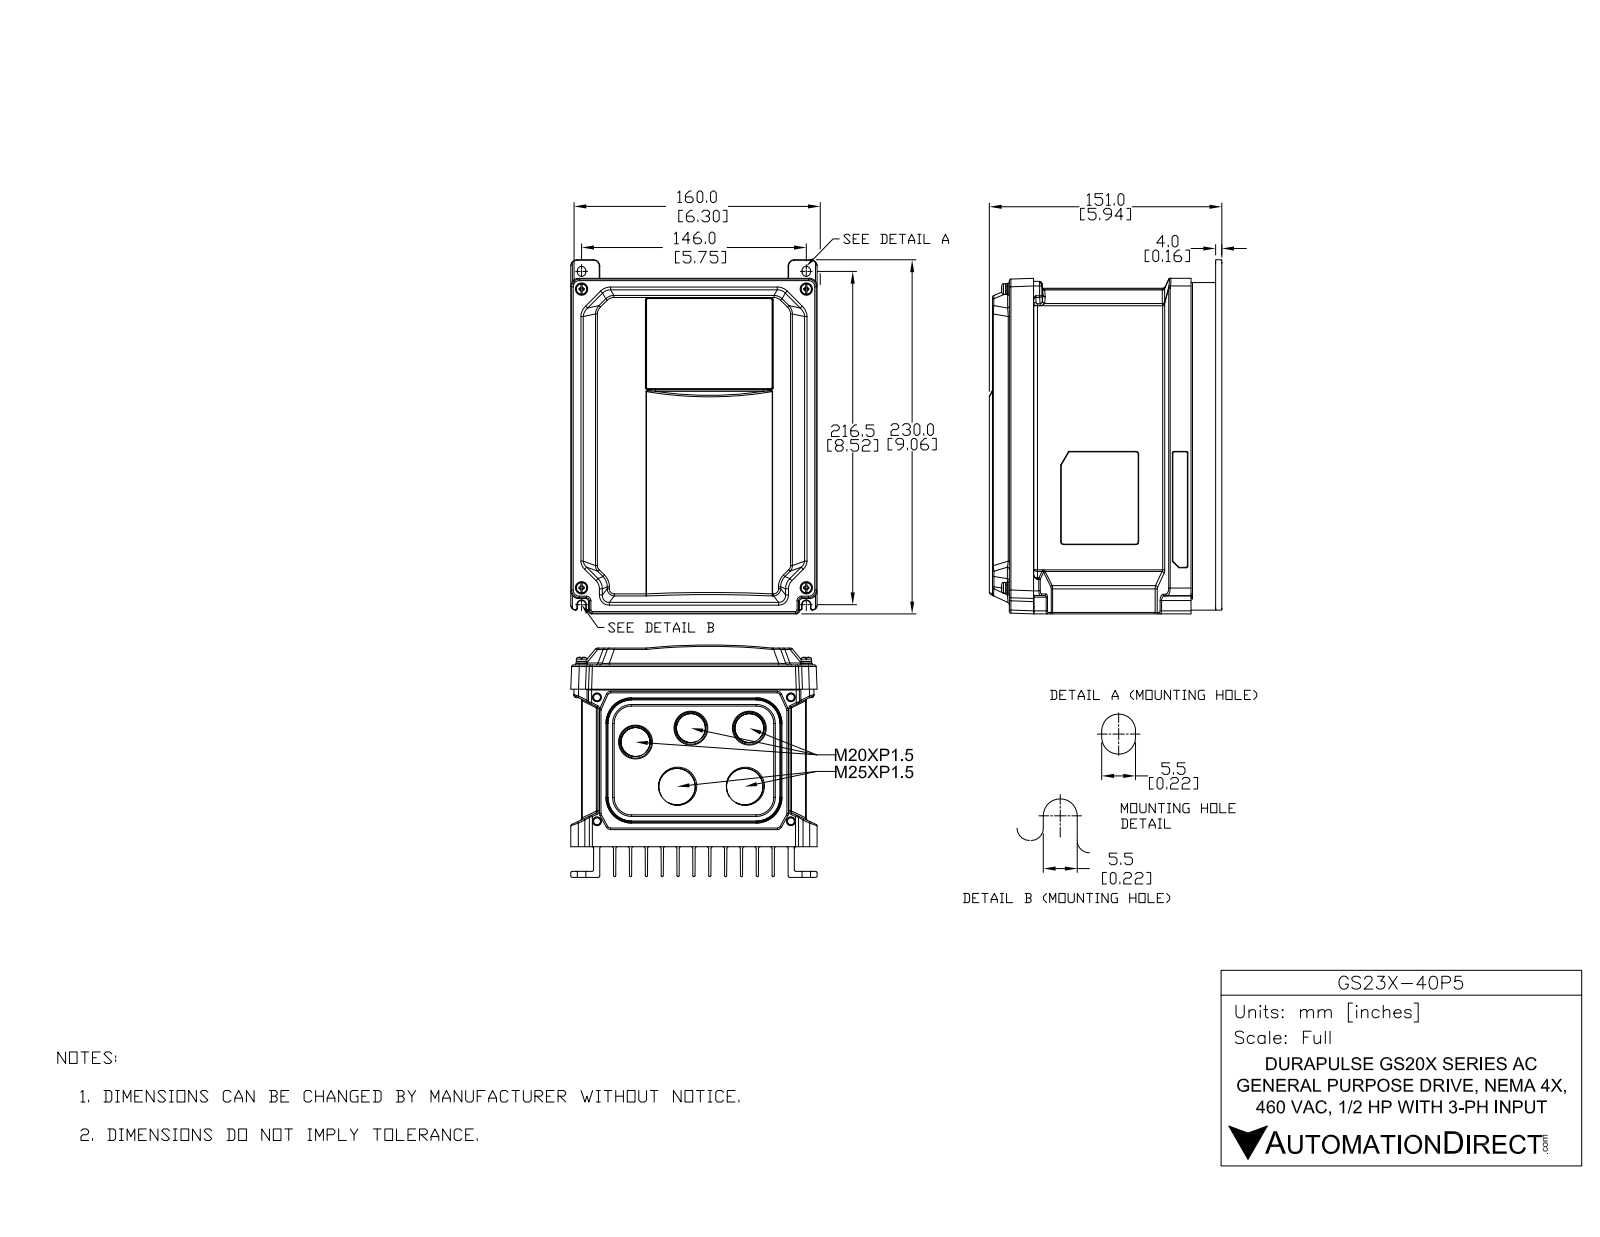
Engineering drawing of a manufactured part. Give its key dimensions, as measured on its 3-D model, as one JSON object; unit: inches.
{"part_name": "GS21X-20P5", "step_written_by": "SolidWorks 2017 (AUTOMOTIVE_DESIGN)", "units": "inches", "bodies": {"solids": 26, "faces": 4979, "planar": 3223, "cylindrical": 1019, "other": 737}, "overall_size": [9.26, 6.299, 5.945], "volume_in3": 53.16, "surface_area_in2": 832.5, "round_holes": [[0.098, 7], [0.165, 4], [0.591, 3], [0.822, 3], [0.827, 3], [0.13, 2], [0.15, 2], [1.015, 2]], "round_bosses_or_shafts": [[0.035, 8], [0.157, 5], [0.268, 4], [0.988, 3], [0.929, 3], [0.78, 3], [0.098, 2], [0.283, 1]], "partial_cylinders_radius": [[0.039, 188], [0.02, 145], [0.012, 114], [0.059, 71], [0.079, 40], [0.004, 28], [0.118, 24], [0.197, 17]], "face_to_face_distances": [0.406, 0.811, 1.217, 1.622, 2.028, 2.433, 2.839, 0.394, 3.244, 0.157], "hole_center_spacings": [0.236, 3.15, 4.961, 6.339, 8.049, 0.472, 0.495, 0.539]}
